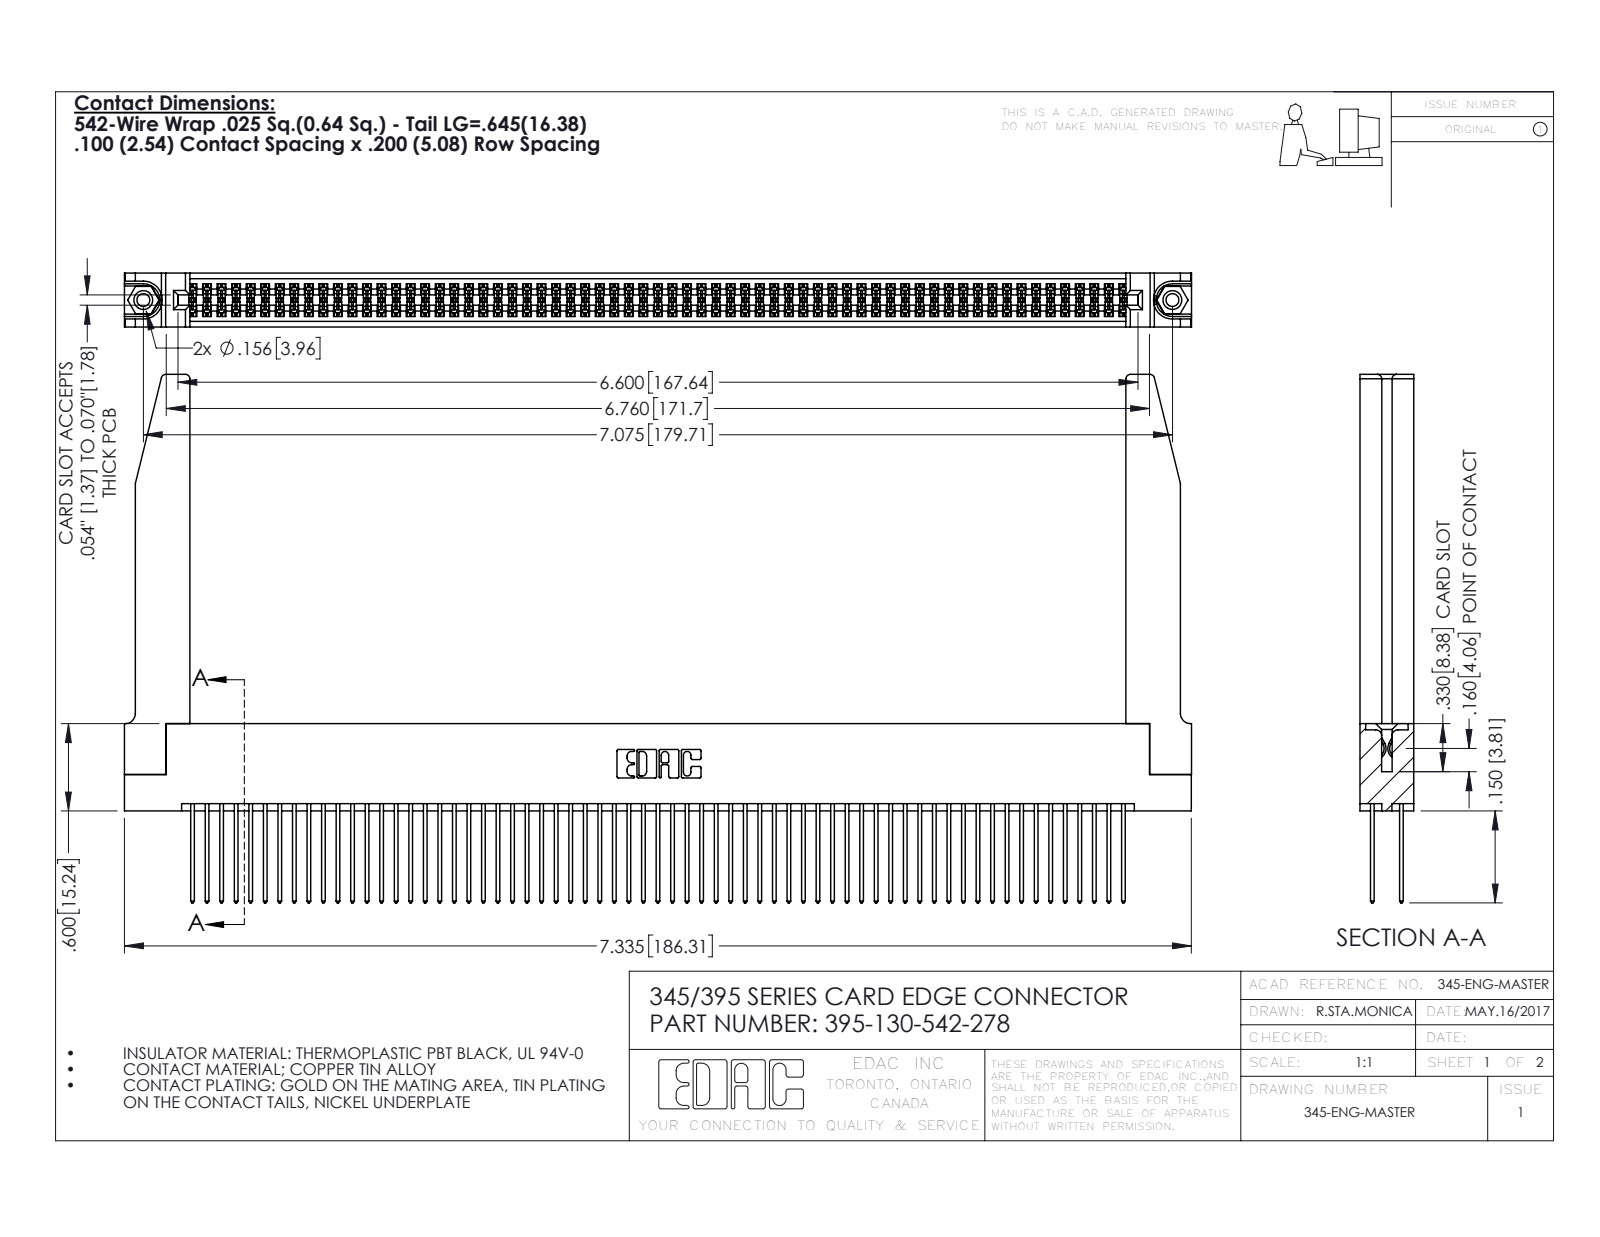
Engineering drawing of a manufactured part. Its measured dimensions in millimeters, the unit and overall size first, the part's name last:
Units: millimetres
Overall size (bounding box): 186.3 × 92.3 × 9.4
Round holes (diameter × count): ⌀2.3 ×2, ⌀3.2 ×2, ⌀4 ×2, ⌀1.6 ×1
Round bosses / shafts (diameter × count): ⌀3.9 ×2
Partial cylindrical surfaces — rounded edges, fillets, slot ends (radius × count): R0.2 ×195, R0.3 ×130, R0.3 ×22, R0.8 ×8, R0.2 ×6, R0.8 ×6, R0.7 ×3, R0.4 ×2
Main face-to-face distances: 1.8, 7.6, 5.1, 9.4, 2.5, 6.9, 0.6, 5.7, 4.4, 3.8
Hole centre spacings: 6.9, 173.7, 179.7
Volume: 26 690 mm³ · Surface area: 38 080 mm²
Bodies: 135 solids, 6860 faces (4512 planar, 2296 cylindrical, 52 other)
Part name (STEP PRODUCT): 345-220-078_345-220-078; 345-250-001_345-250-001-102; 395-130-542-278; 345-292-001_345-293-142 (+1 more)
STEP written by: SolidWorks 2016 (CONFIG_CONTROL_DESIGN)
